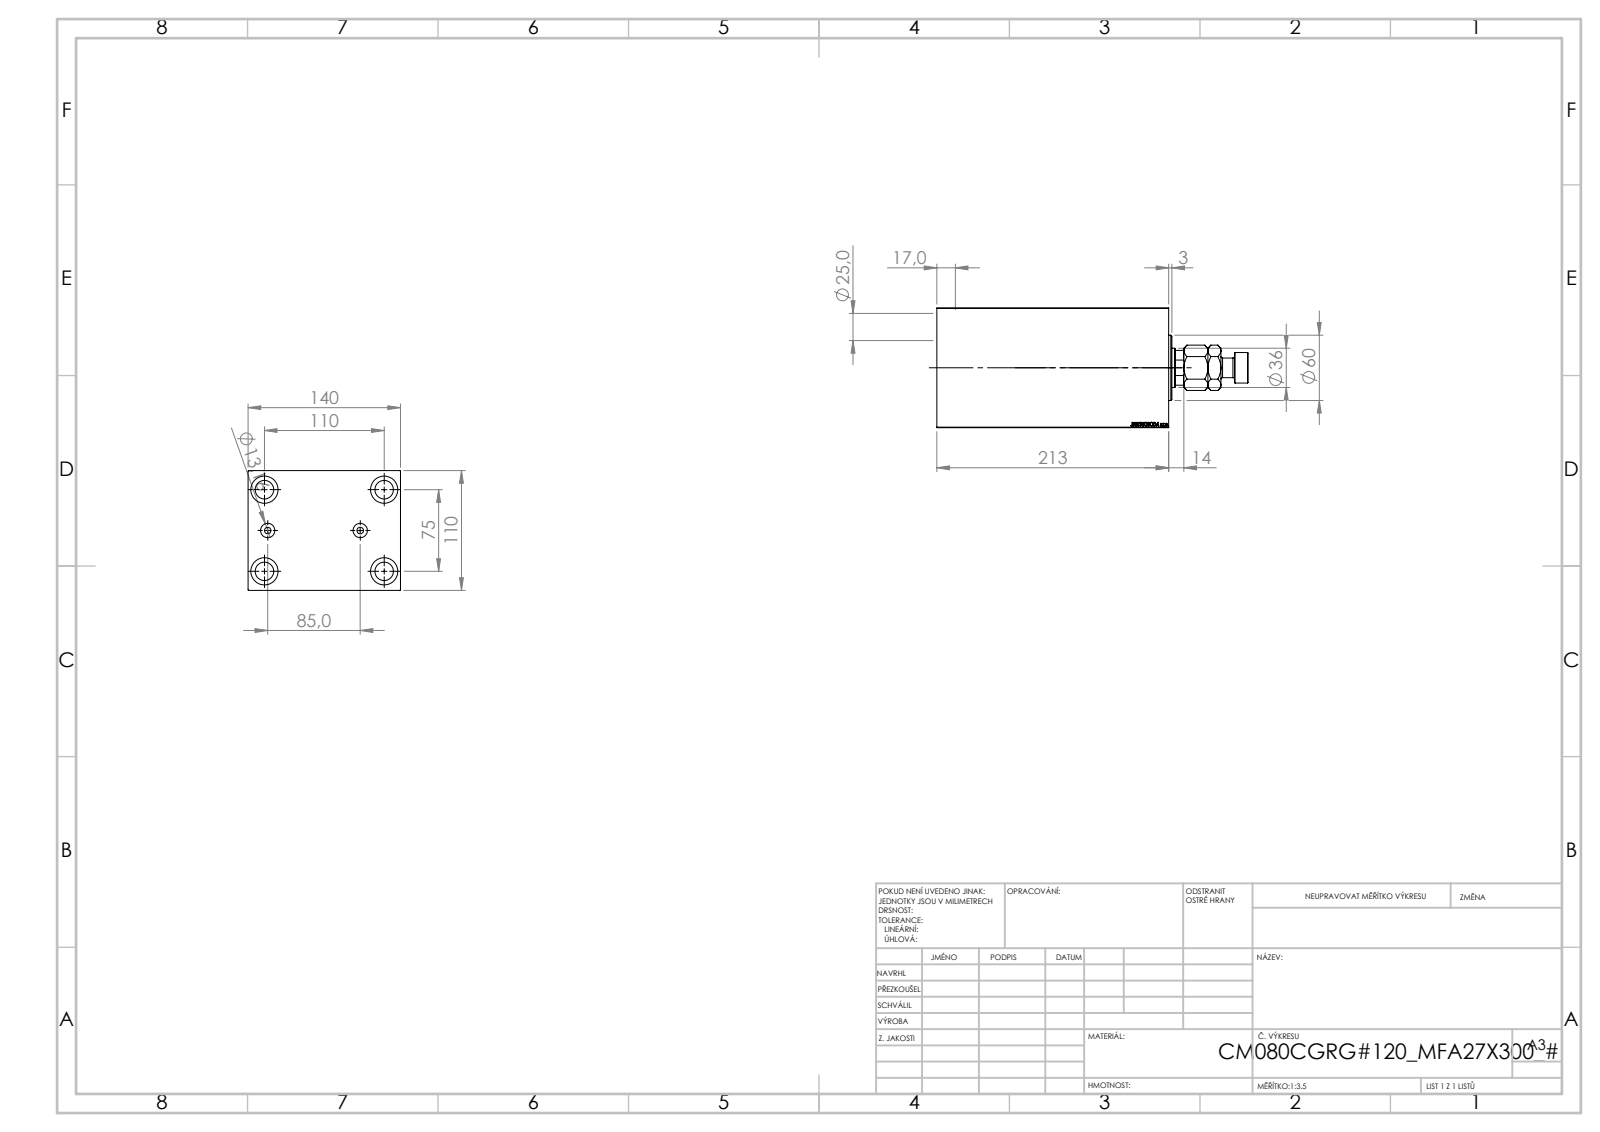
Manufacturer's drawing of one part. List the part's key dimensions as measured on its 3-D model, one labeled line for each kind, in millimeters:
Part name (STEP PRODUCT): V450CM_C_VCP; MFA; V450CM_VC_B; V450CM_C_Body
STEP written by: SolidWorks 2019 (CONFIG_CONTROL_DESIGN)
Units: millimetres
Bodies: 4 solids, 915 faces (427 planar, 62 cylindrical, 426 other)
Overall size (bounding box): 286 × 140 × 110
Volume: 2 606 000 mm³ · Surface area: 312 223 mm²
Round holes (diameter × count): ⌀17 ×4, ⌀25 ×4, ⌀6 ×2, ⌀13.16 ×2, ⌀25.5 ×1, ⌀36 ×1, ⌀39.5 ×1, ⌀80 ×1, ⌀82 ×1, ⌀87 ×1
Round bosses / shafts (diameter × count): ⌀60 ×1, ⌀28 ×1, ⌀18 ×1
Partial cylindrical surfaces — rounded edges, fillets, slot ends (radius × count): R17.5 ×1
Main face-to-face distances: 110, 140, 213, 192, 21, 37.3, 154.7, 175.7, 157.3, 120
Hole centre spacings: 39.53, 66.57, 104.46, 42.5, 75, 110, 133.14, 85
